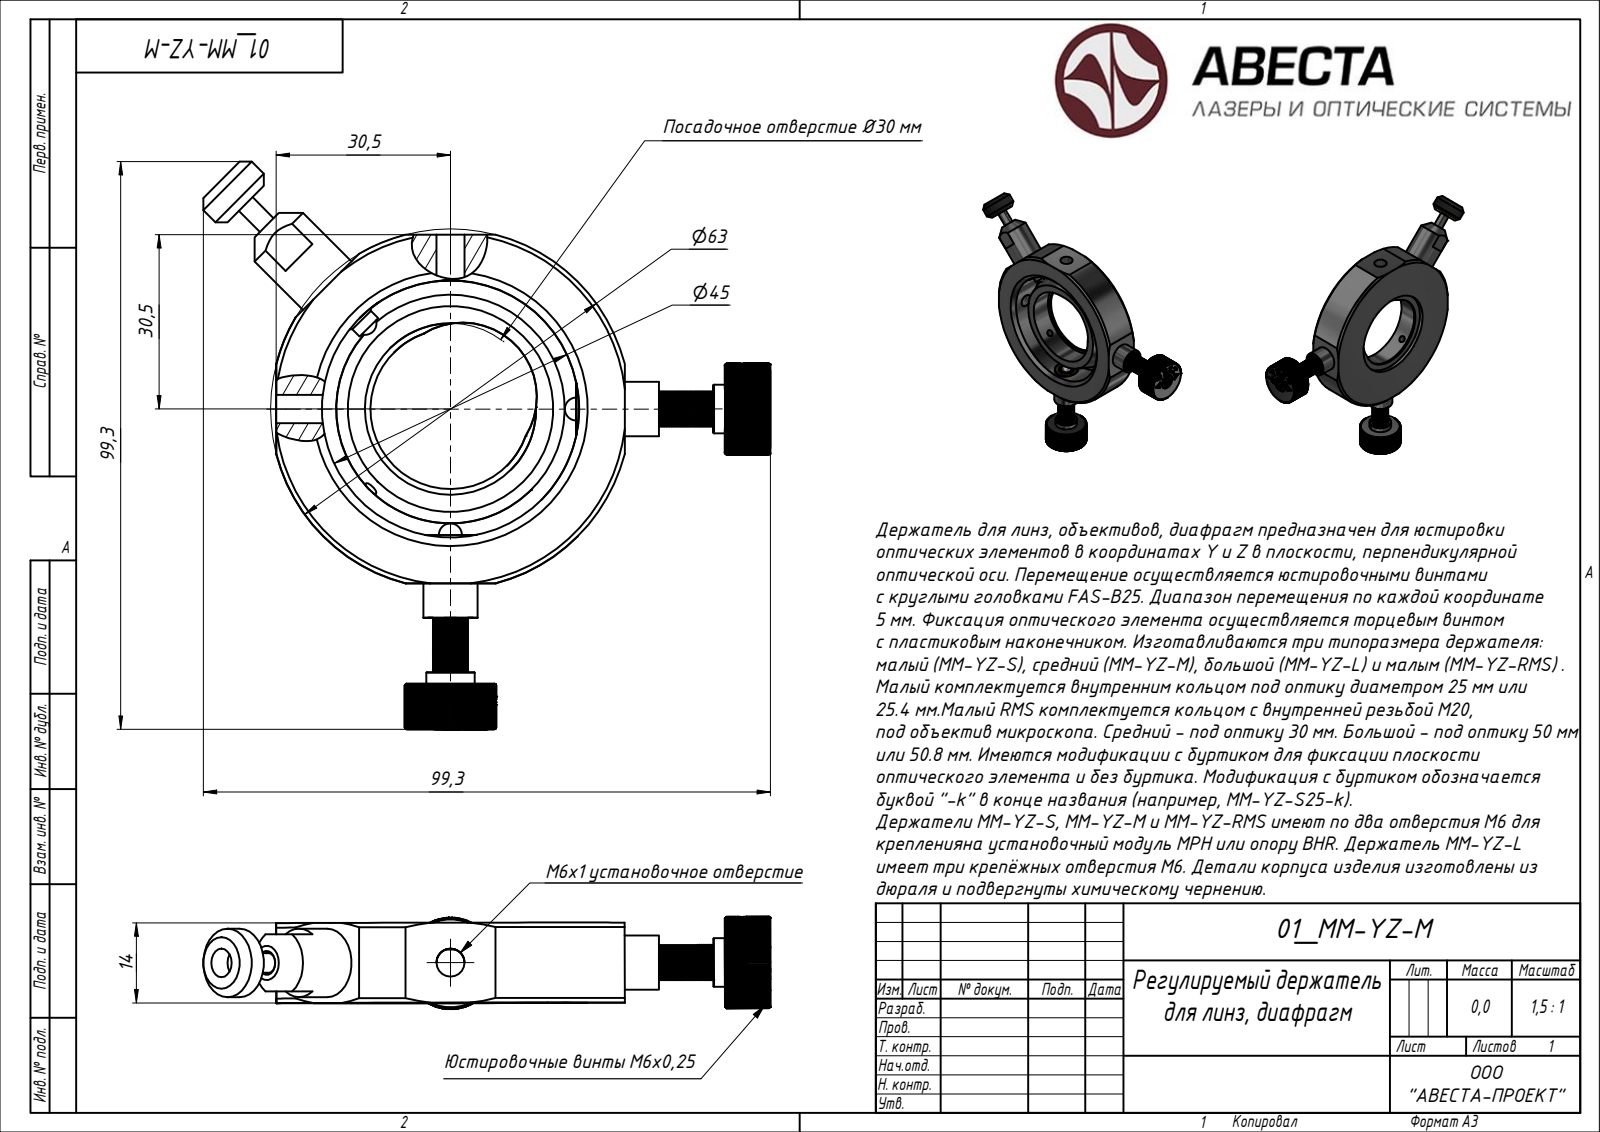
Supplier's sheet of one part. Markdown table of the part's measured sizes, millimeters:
| quantity | value |
| --- | --- |
| STEP written by | ST-DEVELOPER v15 (AUTOMOTIVE_DESIGN) |
| units | millimeters |
| bodies | 14 solids, 578 faces (264 planar, 0 cylindrical, 314 other) |
| overall size | 101.04 × 88.67 × 16.17 |
| volume | 32 005 mm³ |
| surface area | 20 326 mm² |
| main face-to-face distances | 14, 12.5, 1.5, 1.52, 12.48, 60.98, 24.49, 85.47, 3.78, 8.7 |
